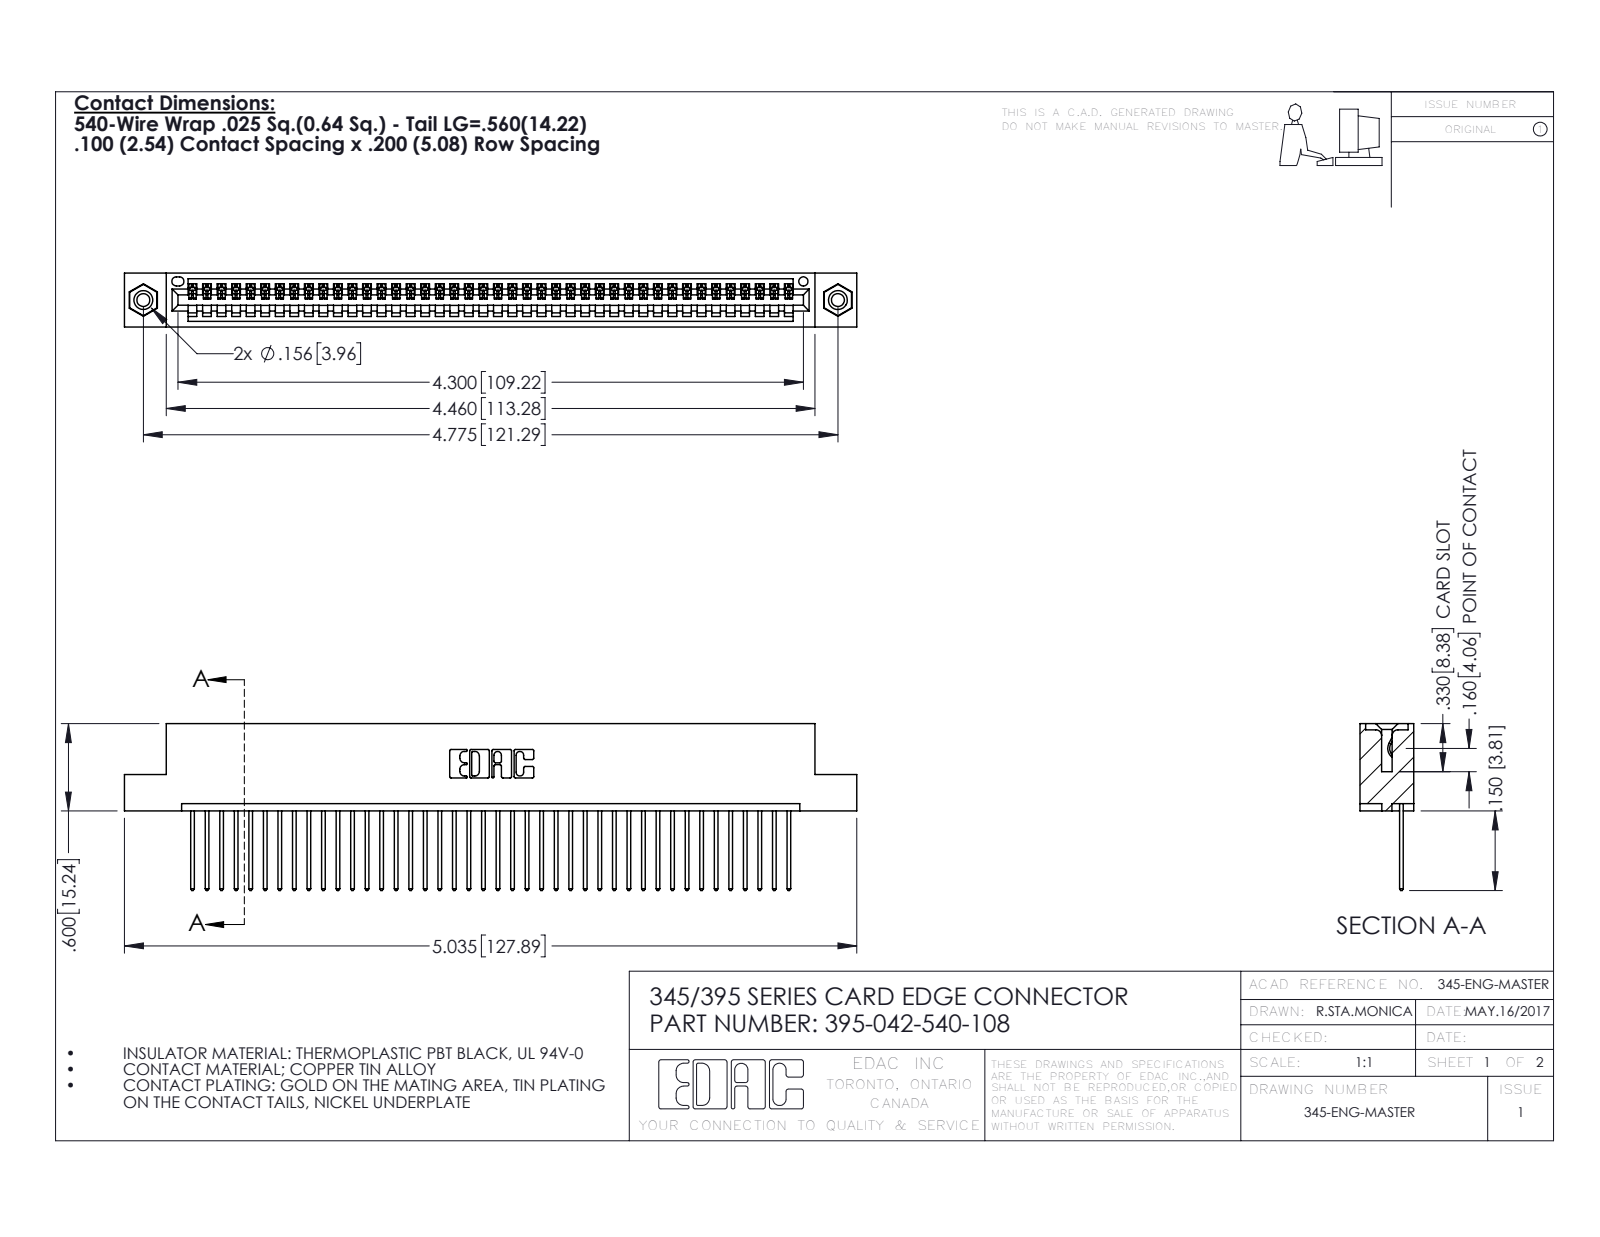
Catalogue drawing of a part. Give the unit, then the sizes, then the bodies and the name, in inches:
Units: inches
Overall size (bounding box): 5.035 × 1.147 × 0.37
Round holes (diameter × count): ⌀0.089 ×2, ⌀0.125 ×2, ⌀0.156 ×2, ⌀0.064 ×1
Round bosses / shafts (diameter × count): ⌀0.155 ×2
Partial cylindrical surfaces — rounded edges, fillets, slot ends (radius × count): R0.006 ×84, R0.01 ×84, R0.01 ×22, R0.007 ×6, R0.031 ×6, R0.026 ×3, R0.031 ×2, R0.04 ×2
Main face-to-face distances: 0.072, 0.298, 0.37, 0.2, 0.098, 0.272, 0.025, 0.225, 0.149, 0.072
Hole centre spacings: 0.27, 4.539, 4.775
Volume: 0.744 in³ · Surface area: 25.79 in²
Bodies: 45 solids, 2622 faces (1792 planar, 814 cylindrical, 16 other)
Part name (STEP PRODUCT): 395-042-540-108; 345-292-001_345-293-140; 345 Part_Flush Mounting Lugs - 0.156 Dia-TI; 345-250-001_345-250-003-102
STEP written by: SolidWorks 2016 (CONFIG_CONTROL_DESIGN)
